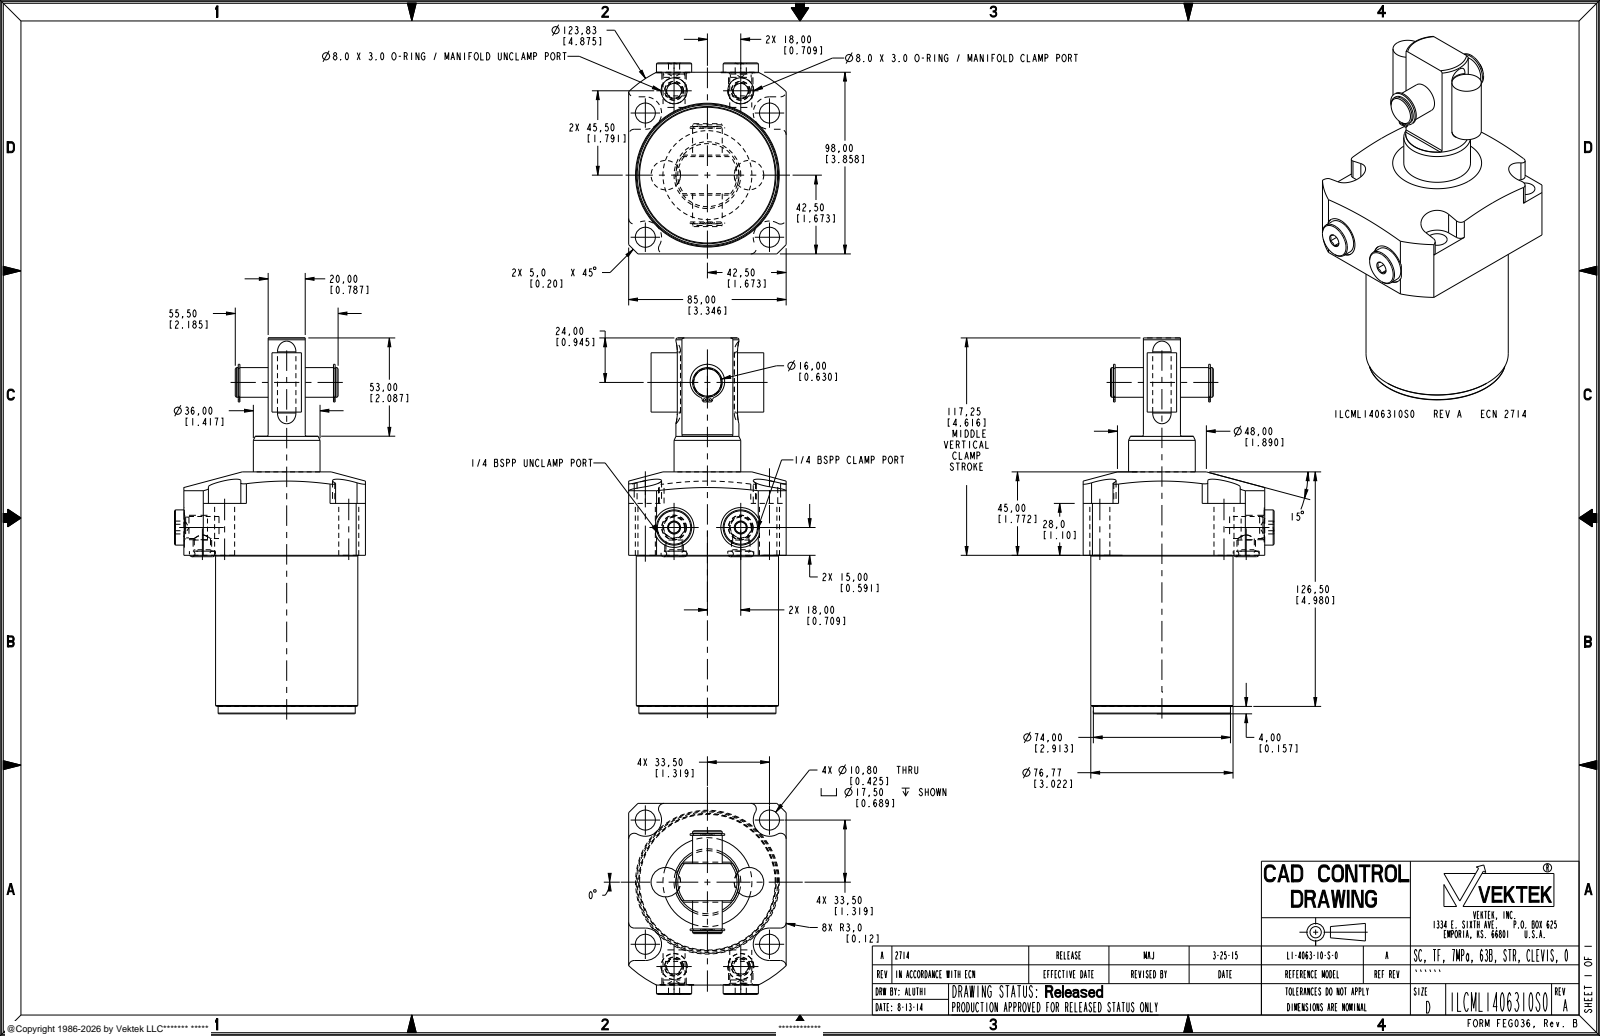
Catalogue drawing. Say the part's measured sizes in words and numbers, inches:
The part is named "ILCML1406310S0". Its 3-D file was written by "PRO/ENGINEER BY PARAMETRIC TECHNOLOGY CORPORATION, 2013320 (AUTOMOTIVE_DESIGN)". It is 5 solids with 237 faces: 85 planar, 104 cylindrical and 48 other. Overall it measures 7.982 by 4.057 by 3.346 inches. Its volume is 47.7 cubic inches and its surface area 113.1 square inches. Round holes: 4 of diameter 0.425, 2 of diameter 0.047, 2 of diameter 0.236, 2 of diameter 0.344, 2 of diameter 0.468, 2 of diameter 0.551, 2 of diameter 0.846, 1 of diameter 0.61. Round bosses or shafts: 2 of diameter 0.748, 2 of diameter 0.625, 2 of diameter 0.518, 2 of diameter 0.441, 2 of diameter 0.394, 1 of diameter 3.022, 1 of diameter 2.913, 1 of diameter 1.417. Partial cylindrical surfaces (rounded edges, fillets, slot ends): 8 of radius 0.118, 4 of radius 0.344, 2 of radius 0.031, 2 of radius 0.047, 2 of radius 0.053, 2 of radius 0.313, 1 of radius 2.437. The main face-to-face distances are 3.346, 3.366, 2.067, 3.858, 1.28, 2.579, 0.787, 1.791, 1.772, 1.102. The hole center spacings are 2.638, 0.374, 0.772, 1.417, 2.082, 2.788, 2.82, 3.161.
